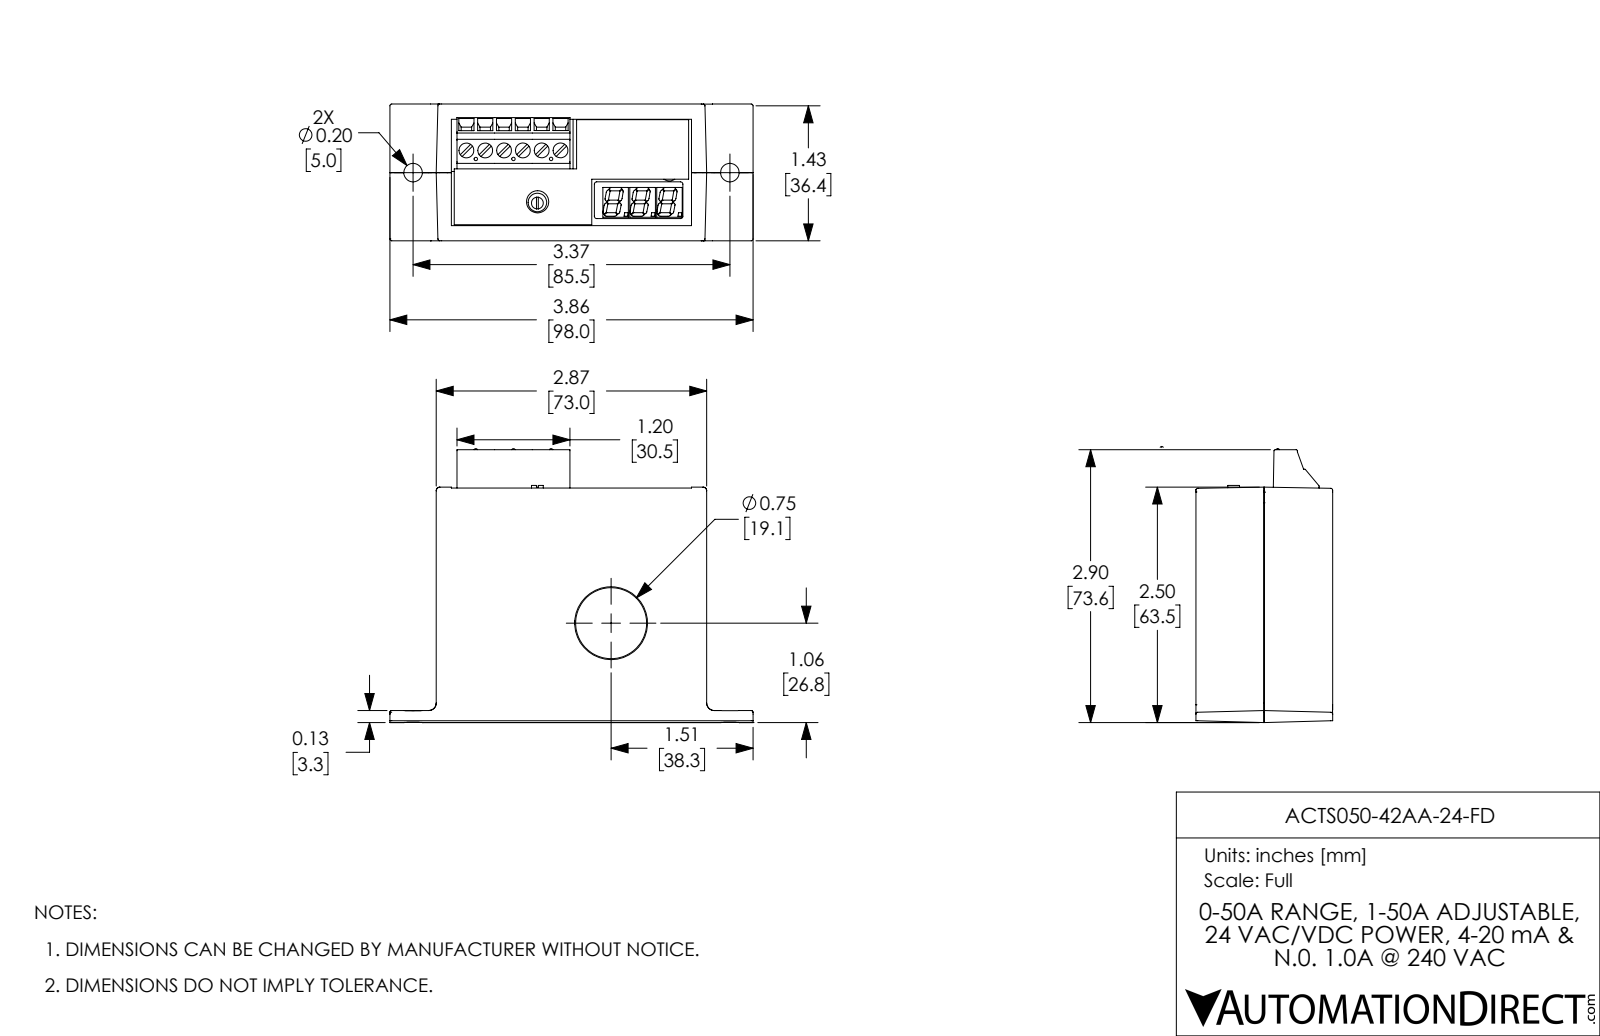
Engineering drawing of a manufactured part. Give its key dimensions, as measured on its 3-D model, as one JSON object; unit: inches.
{"part_name": "ACTS050-42AA-24-FD", "step_written_by": "SolidWorks 2017 (AUTOMOTIVE_DESIGN)", "units": "inches", "bodies": {"solids": 4, "faces": 694, "planar": 498, "cylindrical": 113, "other": 83}, "overall_size": [3.858, 2.909, 1.453], "volume_in3": 9.871, "surface_area_in2": 71.12, "round_holes": [[0.157, 6], [0.197, 5], [0.059, 4], [0.26, 2], [0.154, 1], [0.198, 1], [0.236, 1], [0.774, 1]], "round_bosses_or_shafts": [[0.126, 1]], "partial_cylinders_radius": [[0.02, 18], [0.012, 14], [0.025, 5], [0.039, 4], [0.079, 4], [0.01, 2], [0.077, 2]], "face_to_face_distances": [0.11, 1.343, 1.453, 2.874, 0.059, 0.069, 0.062, 0.072, 0.013, 0.072], "hole_center_spacings": [0.2, 0.4, 0.697, 0.6, 0.37, 0.604, 0.789, 0.8]}
